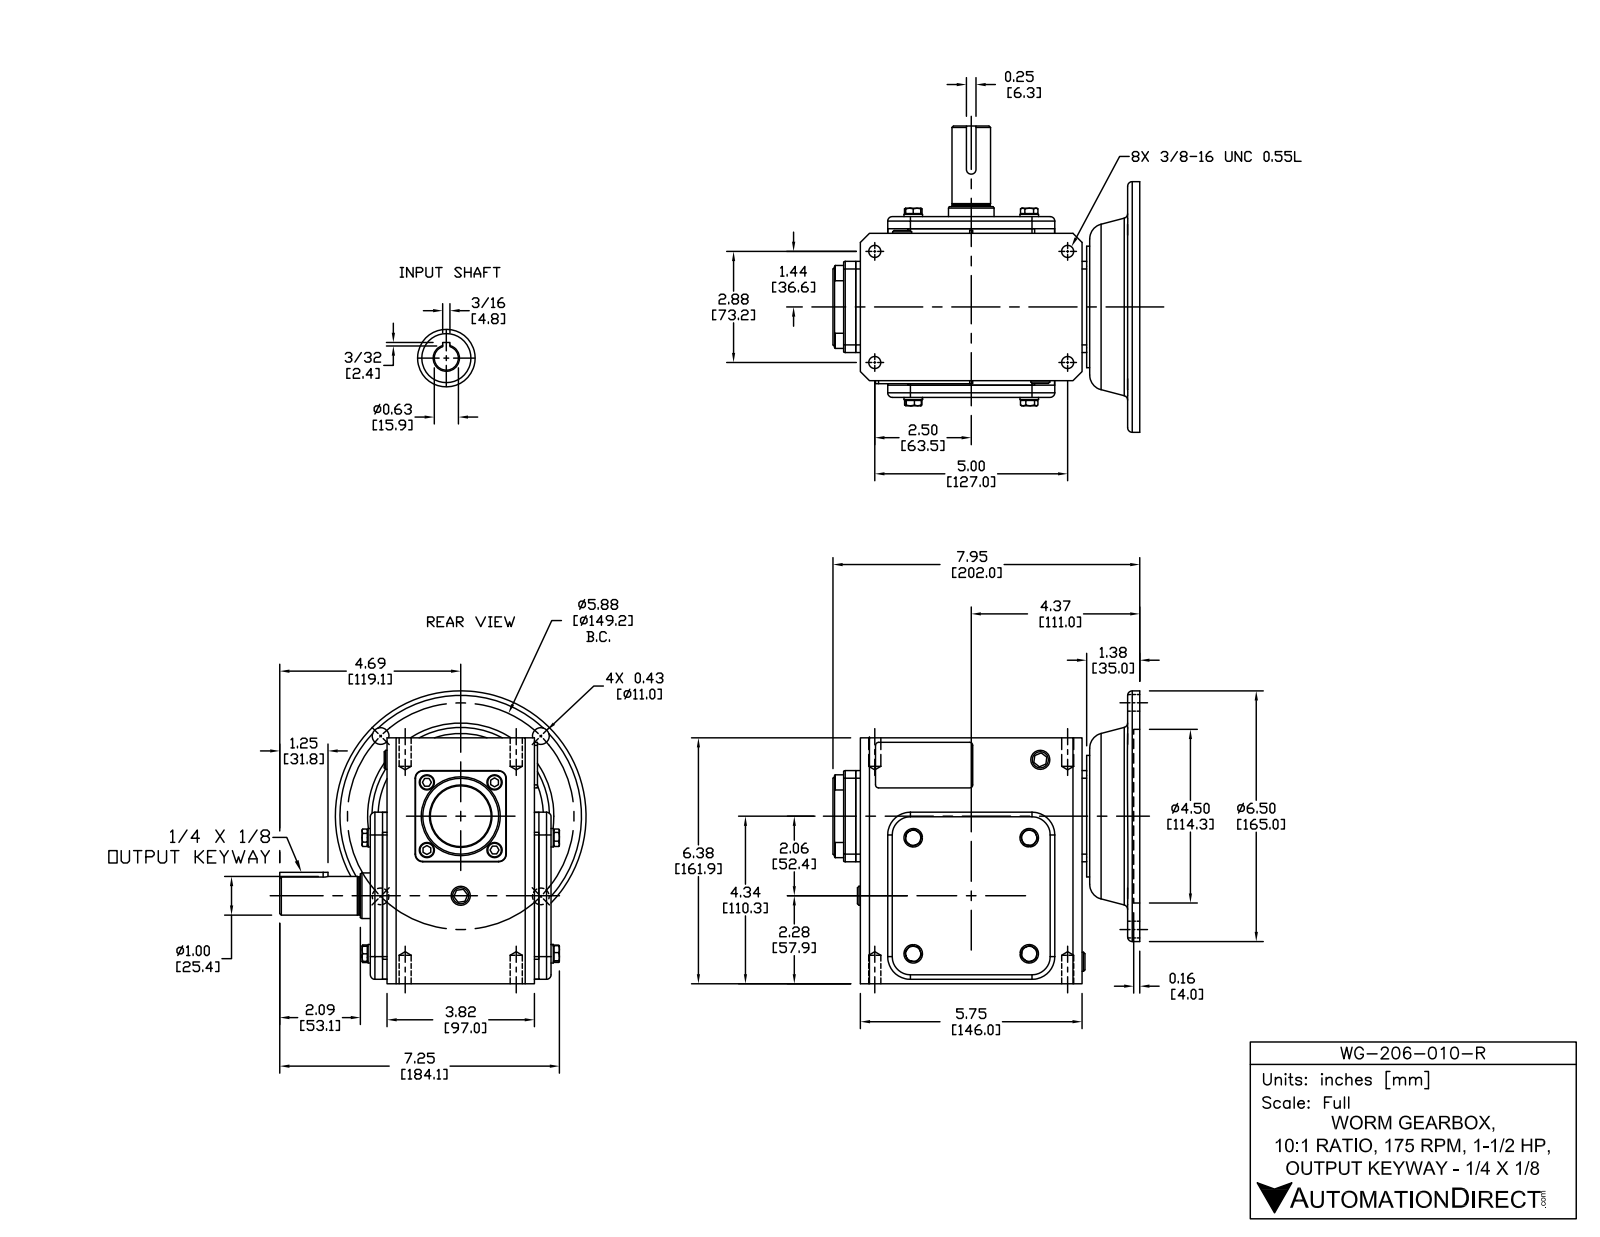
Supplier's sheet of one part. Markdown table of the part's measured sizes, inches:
| quantity | value |
| --- | --- |
| part name | WG-206-010-R |
| STEP written by | SolidWorks 2015 (CONFIG_CONTROL_DESIGN) |
| units | inches |
| bodies | 43 solids, 610 faces (300 planar, 182 cylindrical, 128 other) |
| overall size | 7.953 × 7.938 × 7.591 |
| volume | 171.8 in³ |
| surface area | 407.7 in² |
| round holes (diameter × count) | 0.313 × 4, 0.406 × 4, 0.591 × 1, 0.625 × 1, 1.181 × 1, 1.457 × 1, 1.654 × 1, 3.543 × 1, 4.5 × 1 |
| round bosses / shafts (diameter × count) | 0.394 × 8, 0.48 × 4, 6.496 × 1, 3.15 × 1, 2.047 × 1, 1.575 × 1, 1.181 × 1, 1.142 × 1 |
| partial cylindrical surfaces (radius × count) | 0.079 × 8, 0.118 × 8, 0.197 × 4, 0.591 × 4, 0.02 × 2, 0.039 × 2, 0.125 × 1, 2.717 × 1 |
| main face-to-face distances | 0.315, 0.118, 4.055, 4.37, 0.433, 4.252, 3.937, 6.375, 4.685, 0.709 |
| hole center spacings | 2.937, 4.154, 2.077, 2.88, 4.631, 5, 5.77, 5.875 |
